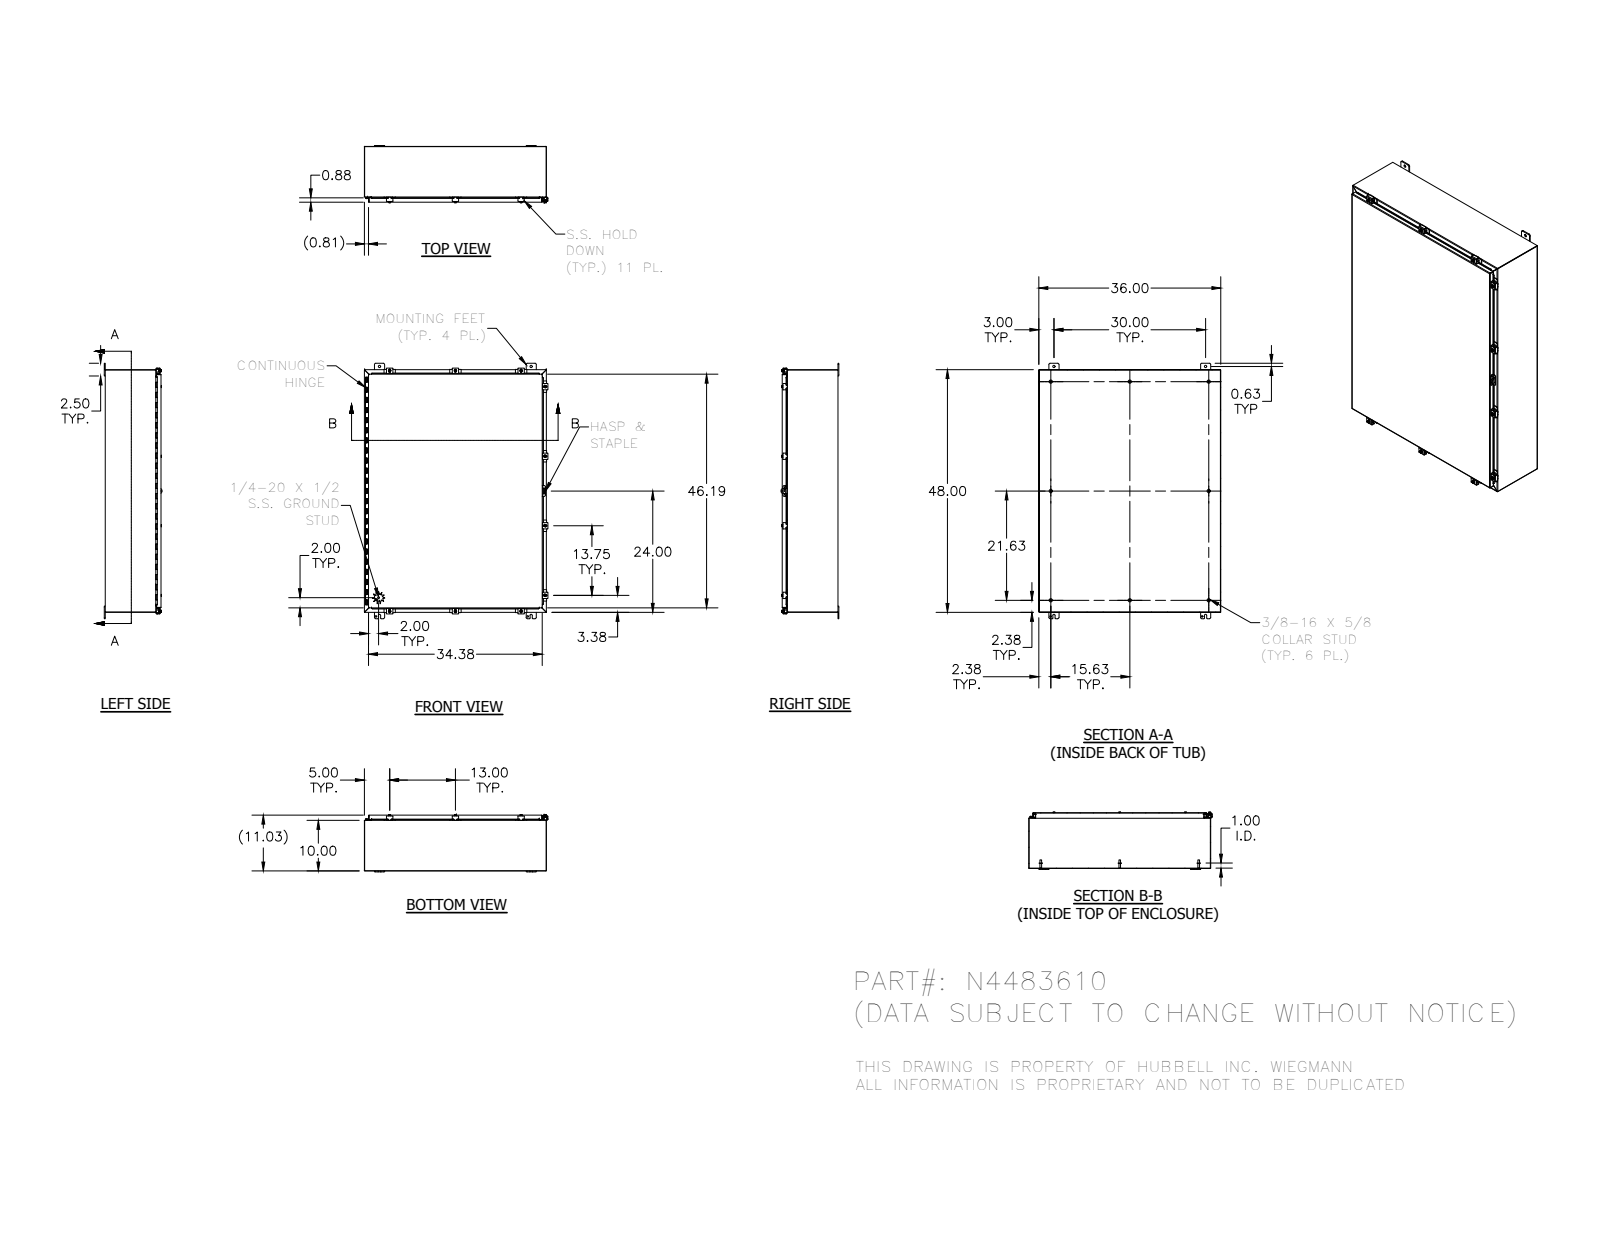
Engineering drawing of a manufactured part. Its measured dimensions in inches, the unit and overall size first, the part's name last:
Units: inches
Overall size (bounding box): 50.5 × 36.311 × 11.41
Round holes (diameter × count): ⌀0.211 ×10, ⌀0.281 ×10, ⌀0.3 ×10, ⌀0.313 ×4, ⌀0.438 ×4, ⌀0.11 ×3, ⌀0.125 ×1, ⌀0.156 ×1, ⌀0.5 ×1
Round bosses / shafts (diameter × count): ⌀0.25 ×12, ⌀0.52 ×10, ⌀0.5 ×10, ⌀0.35 ×10, ⌀0.625 ×8, ⌀0.33 ×8, ⌀0.337 ×1, ⌀0.12 ×1
Partial cylindrical surfaces — rounded edges, fillets, slot ends (radius × count): R0.03 ×117, R0.125 ×41, R0.25 ×37, R0.062 ×22, R0.031 ×21, R0.105 ×21, R0.141 ×20, R0.1 ×14
Main face-to-face distances: 0.074, 10.959, 10.885, 11.033, 35.926, 47.926, 35.852, 36, 9.926, 1.033
Hole centre spacings: 1.593, 13, 30, 48, 49.36, 56.604, 13.75, 47.617
Volume: 439.3 in³ · Surface area: 11 624 in²
Bodies: 73 solids, 2720 faces (1105 planar, 1190 cylindrical, 425 other)
Part name (STEP PRODUCT): 46x34_1; 328115P_1; N44836LID_1; 3293_1 (+8 more)
STEP written by: SolidWorks 2014 (AUTOMOTIVE_DESIGN)
